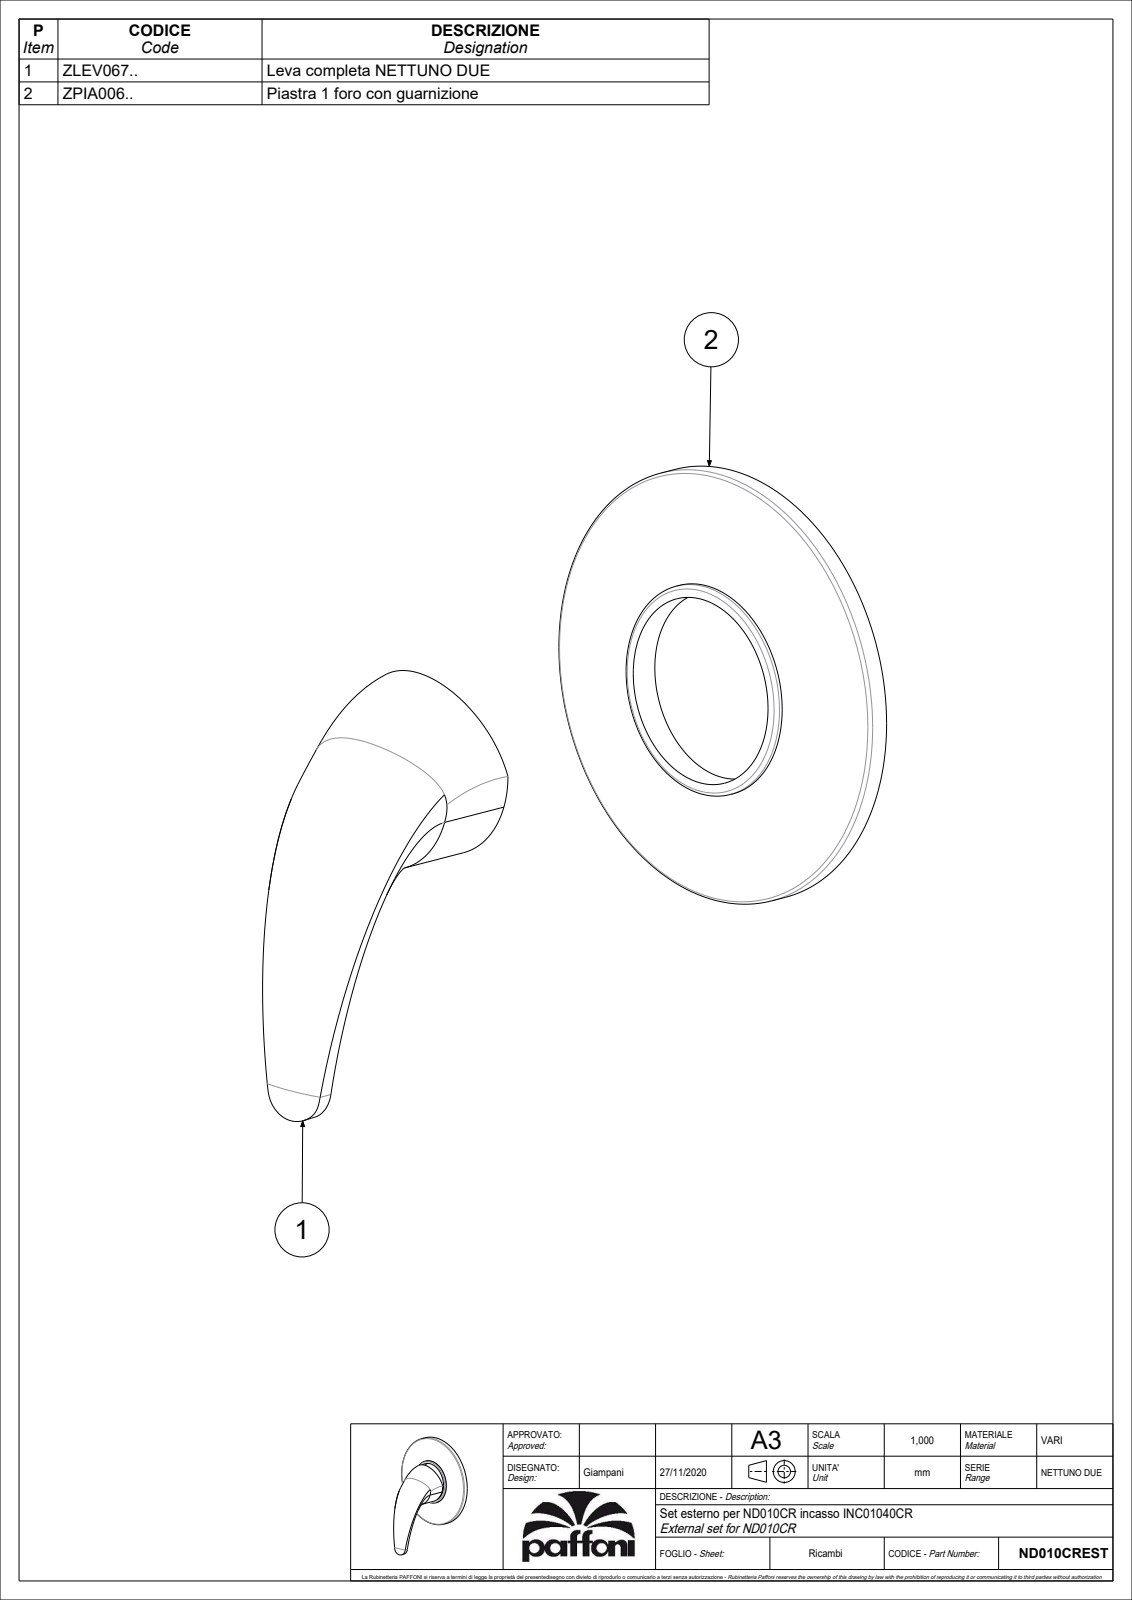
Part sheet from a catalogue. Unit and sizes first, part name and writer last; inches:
Units: inches
Overall size (bounding box): 5.748 × 4.567 × 2.677
Round holes (diameter × count): ⌀0.165 ×1, ⌀0.236 ×1, ⌀0.37 ×1, ⌀1.969 ×1, ⌀4.528 ×1
Round bosses / shafts (diameter × count): ⌀4.567 ×1, ⌀2.224 ×1, ⌀2.165 ×1, ⌀0.197 ×1
Partial cylindrical surfaces — rounded edges, fillets, slot ends (radius × count): R0.154 ×1, R0.157 ×1
Main face-to-face distances: 0.079, 0.315, 0.102, 0.5, 1.388, 1.073, 0.602, 0.433, 0.217, 0.496
Volume: 2.992 in³ · Surface area: 63.12 in²
Bodies: 2 solids, 105 faces (46 planar, 24 cylindrical, 35 other)
Part name (STEP PRODUCT): ND010CREST
STEP written by: CREO PARAMETRIC BY PTC INC, 2020044 (CONFIG_CONTROL_DESIGN)
